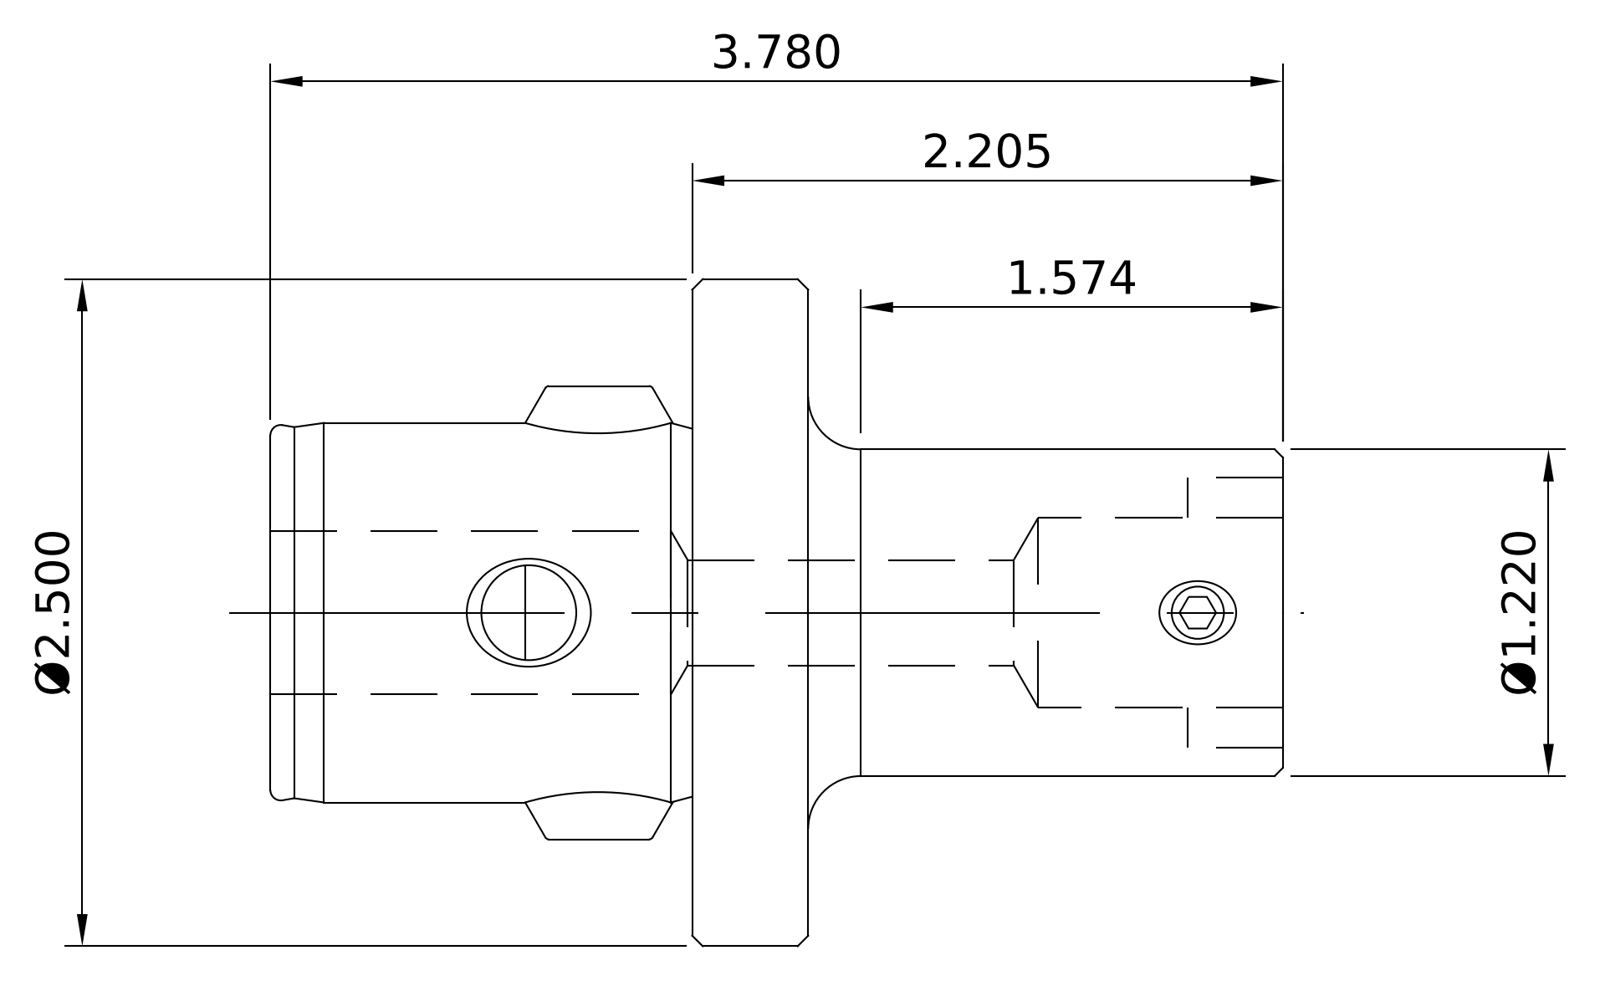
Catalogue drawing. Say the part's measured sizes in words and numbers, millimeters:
The part is named "10.691.50X_10.691.506; 10.690.43X_10.690.433; 691-50XRing_10.691.506Ring; 11.332.631". Its 3-D file was written by "SolidWorks 2016 (AUTOMOTIVE_DESIGN)". It is 4 solids with 148 faces: 41 planar, 49 cylindrical and 58 other. Overall it measures 96 by 63.27 by 63.27 millimeters. Its volume is 96 253 cubic millimeters and its surface area 24 576 square millimeters. Round holes: 2 of diameter 5, 1 of diameter 6.2, 1 of diameter 9, 1 of diameter 10, 1 of diameter 14, 1 of diameter 16, 1 of diameter 18, 1 of diameter 18.5. Round bosses or shafts: 1 of diameter 63.27, 1 of diameter 36, 1 of diameter 31, 1 of diameter 30.6, 1 of diameter 13.9, 1 of diameter 11.9, 1 of diameter 9.9, 1 of diameter 6. Partial cylindrical surfaces (rounded edges, fillets, slot ends): 2 of radius 2.75, 1 of radius 18. The main face-to-face distances are 12, 40, 52, 96, 56, 44, 43, 3, 15.2, 27.8. The hole center spacings are 13.5, 63.45.
